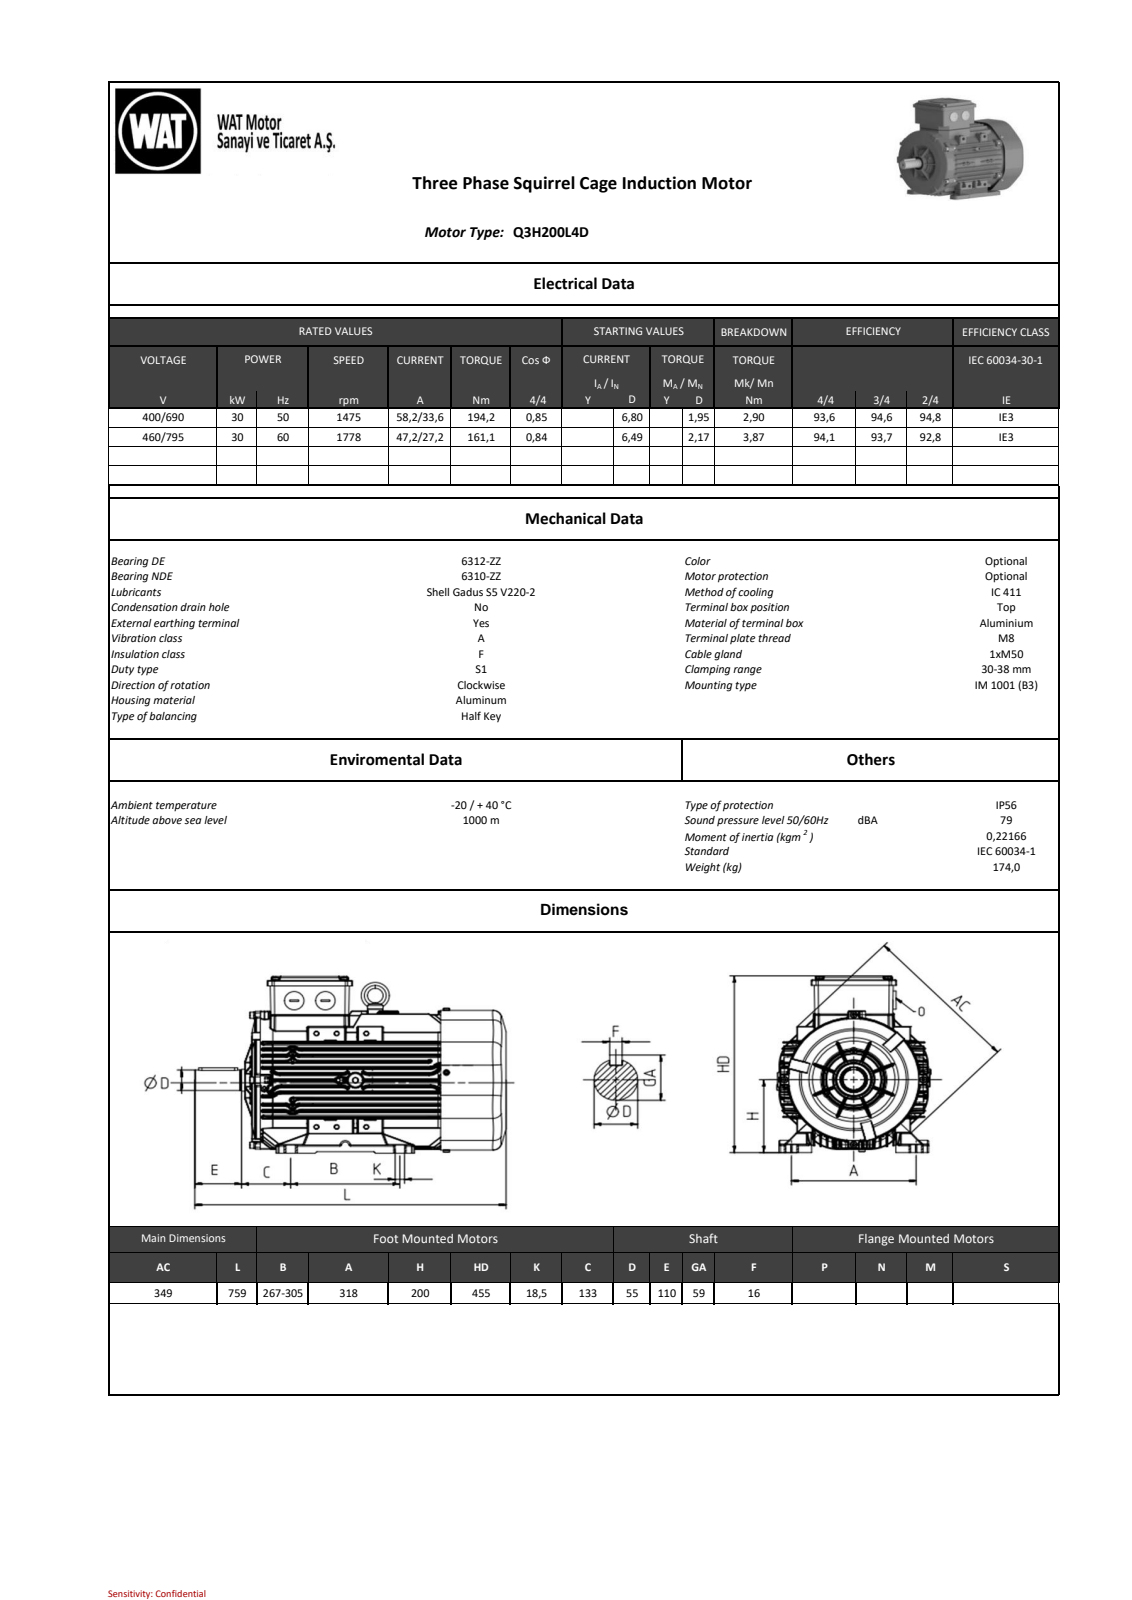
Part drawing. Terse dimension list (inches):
name: model1_objects
written by: SIEMENS PLM Software NX2206.8101 (AUTOMOTIVE_DESIGN)
unit: in
bodies: 0 solids, 14969 faces (3941 planar, 5781 cylindrical, 5247 other)
size: 27.776 × 17.795 × 15.271
holes: 8× ⌀0.22, 4× ⌀0.016, 4× ⌀0.169, 4× ⌀0.217, 4× ⌀0.256, 4× ⌀0.327, 4× ⌀0.411, 3× ⌀0.157, 2× ⌀0.372, 2× ⌀0.986, 2× ⌀1.732, 1× ⌀0.299
bosses: 6× ⌀0.394, 4× ⌀0.713, 4× ⌀0.63, 4× ⌀0.583, 4× ⌀0.512, 4× ⌀0.472, 4× ⌀0.374, 4× ⌀0.315
rounds: 1752× R0.02, 961× R0.039, 903× R0.079, 204× R0.118, 187× R0.059, 122× R0.004, 100× R0.03, 80× R0.157
face distances: 0.047, 0.638, 1.279, 0.641, 0.236, 6.734, 6.844, 5.565, 6.206, 6.094
hole spacings: 5.354, 3.077, 6.691, 6.142, 6.339, 8.964, 2.684, 2.685
